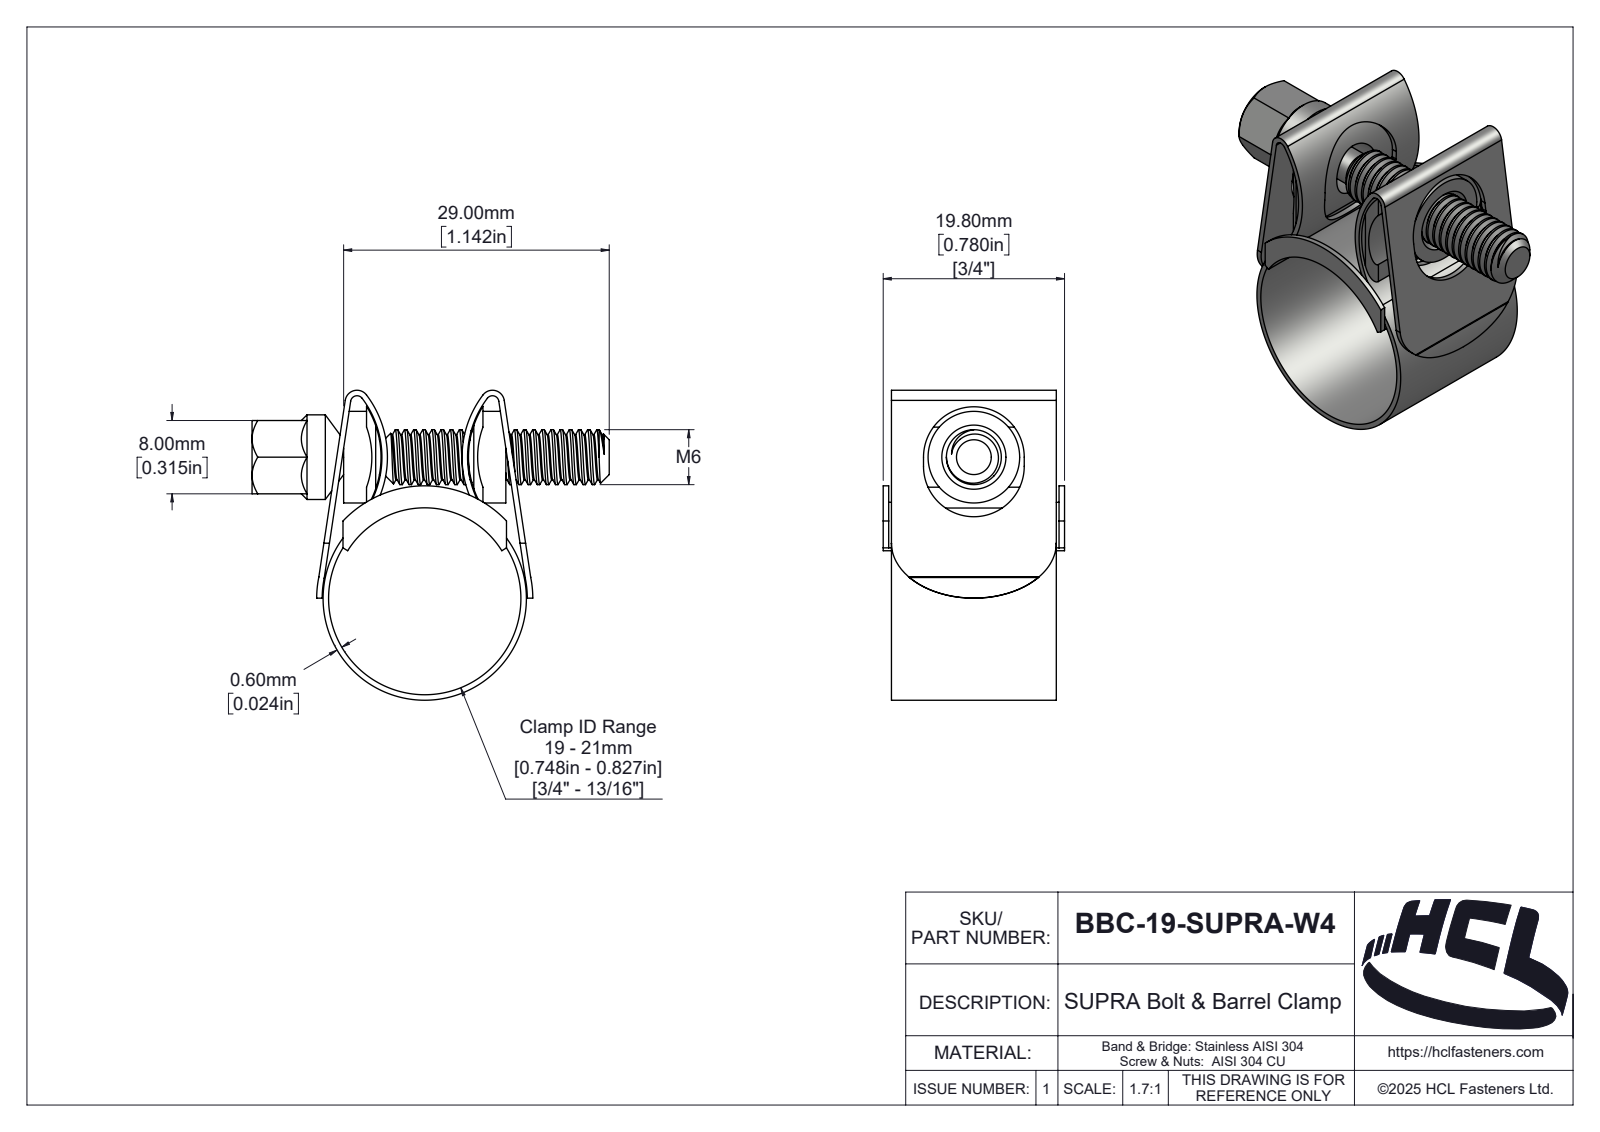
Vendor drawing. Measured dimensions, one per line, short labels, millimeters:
name: BBC-19-SUPRA-W4
written by: SolidWorks 2025 (AUTOMOTIVE_DESIGN)
unit: mm
bodies: 5 solids, 281 faces (44 planar, 157 cylindrical, 80 other)
size: 39 × 33.83 × 19.8
volume: 3 109 mm³; area: 7 134 mm²
holes: 1× ⌀21
bosses: 1× ⌀10, 1× ⌀9.24, 1× ⌀6, 1× ⌀3.8
rounds: 4× R1, 2× R0.7, 2× R1.3, 2× R2, 2× R2.6, 2× R5.5, 2× R9.53, 2× R10.53
face distances: 0.6, 0.9, 18.9, 18, 2.5, 15.22, 8, 19.2, 18.3, 12.72
